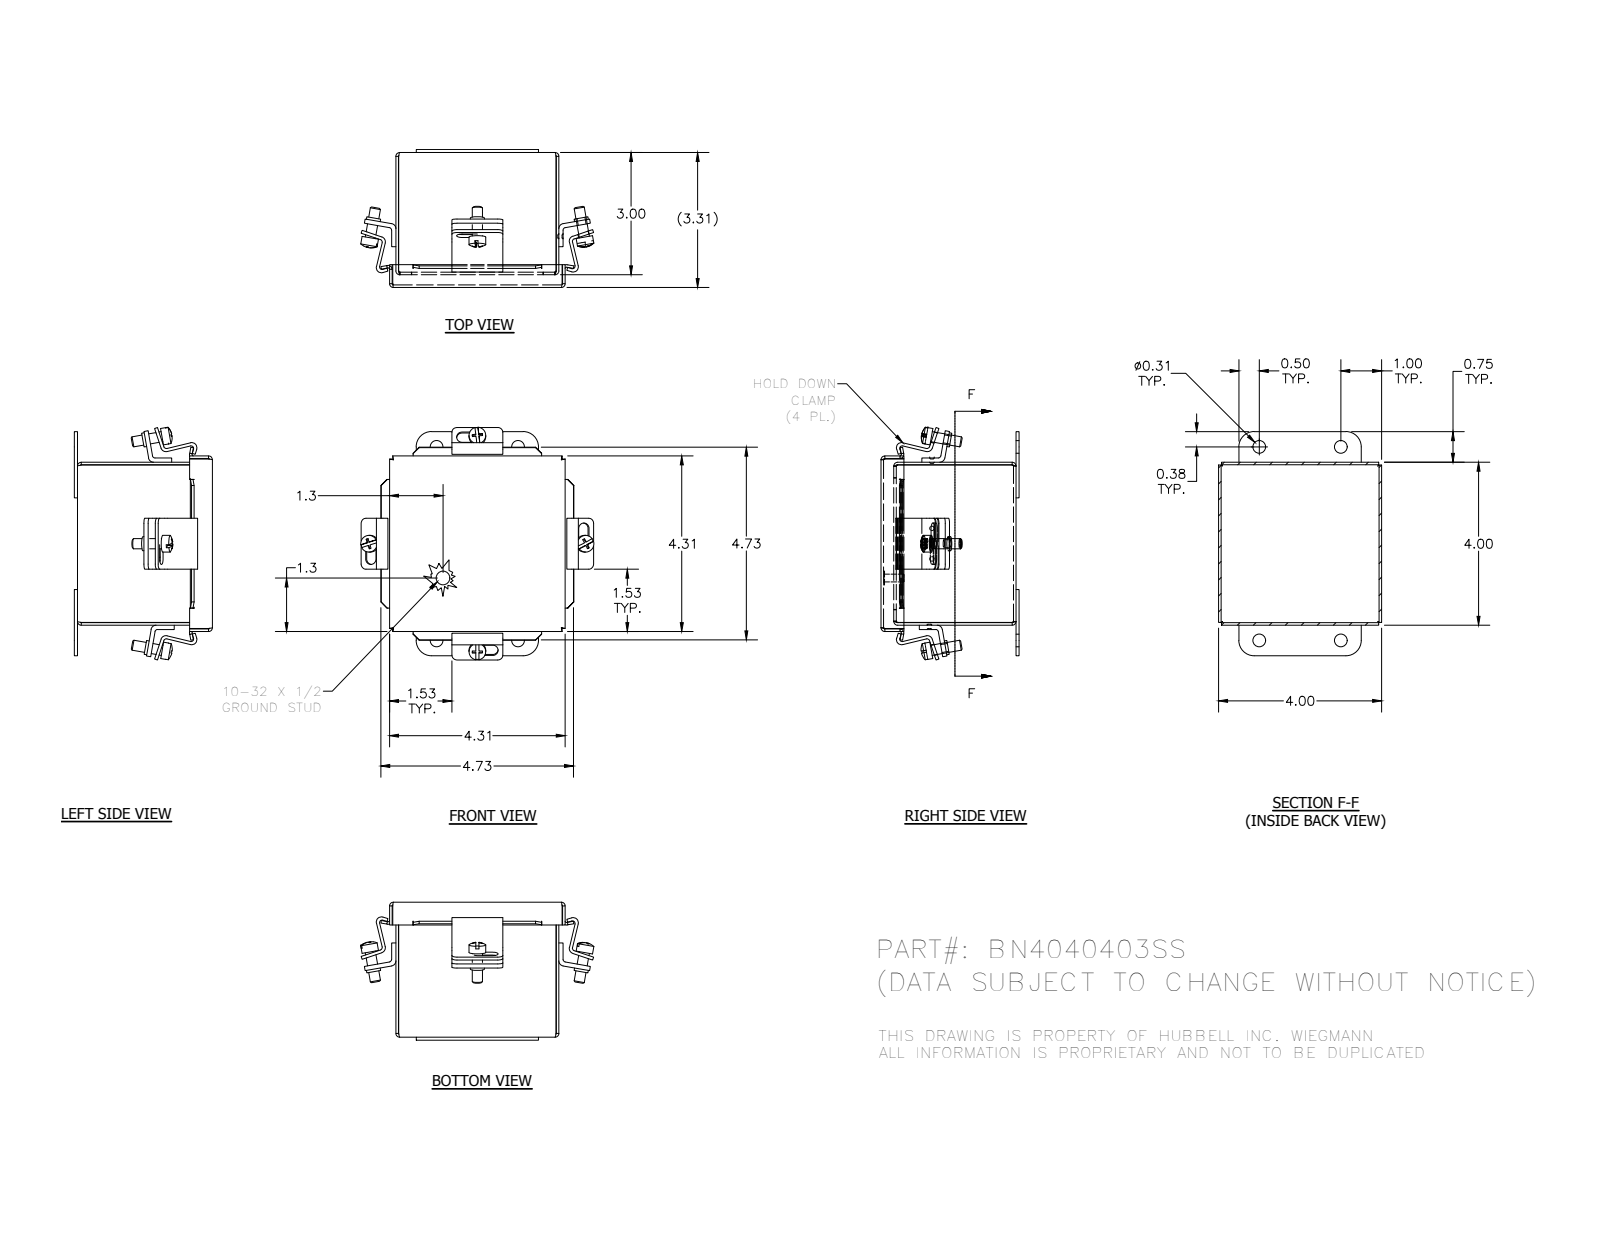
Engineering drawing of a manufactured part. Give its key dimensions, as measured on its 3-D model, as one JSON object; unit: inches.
{"part_name": "BN4040403SS; C2001_1; BN40404SSLID_1; HFW3883_1 (+4 more)", "step_written_by": "SolidWorks 2014 (AUTOMOTIVE_DESIGN)", "units": "inches", "bodies": {"solids": 17, "faces": 529, "planar": 275, "cylindrical": 176, "other": 78}, "overall_size": [5.724, 5.712, 3.388], "volume_in3": 7.988, "surface_area_in2": 247.6, "round_holes": [[0.11, 6], [0.196, 4], [0.31, 4]], "round_bosses_or_shafts": [[0.41, 4], [0.344, 4], [0.25, 4], [0.337, 1], [0.19, 1]], "partial_cylinders_radius": [[0.031, 16], [0.094, 16], [0.125, 16], [0.063, 12], [0.126, 12], [0.133, 8], [0.375, 4]], "face_to_face_distances": [0.063, 3.937, 3.25, 4, 3.875, 3.313, 3.187, 0.075, 0.155, 4.093], "hole_center_spacings": [0.75, 0.063, 0.753, 2, 4.75, 5.154]}
